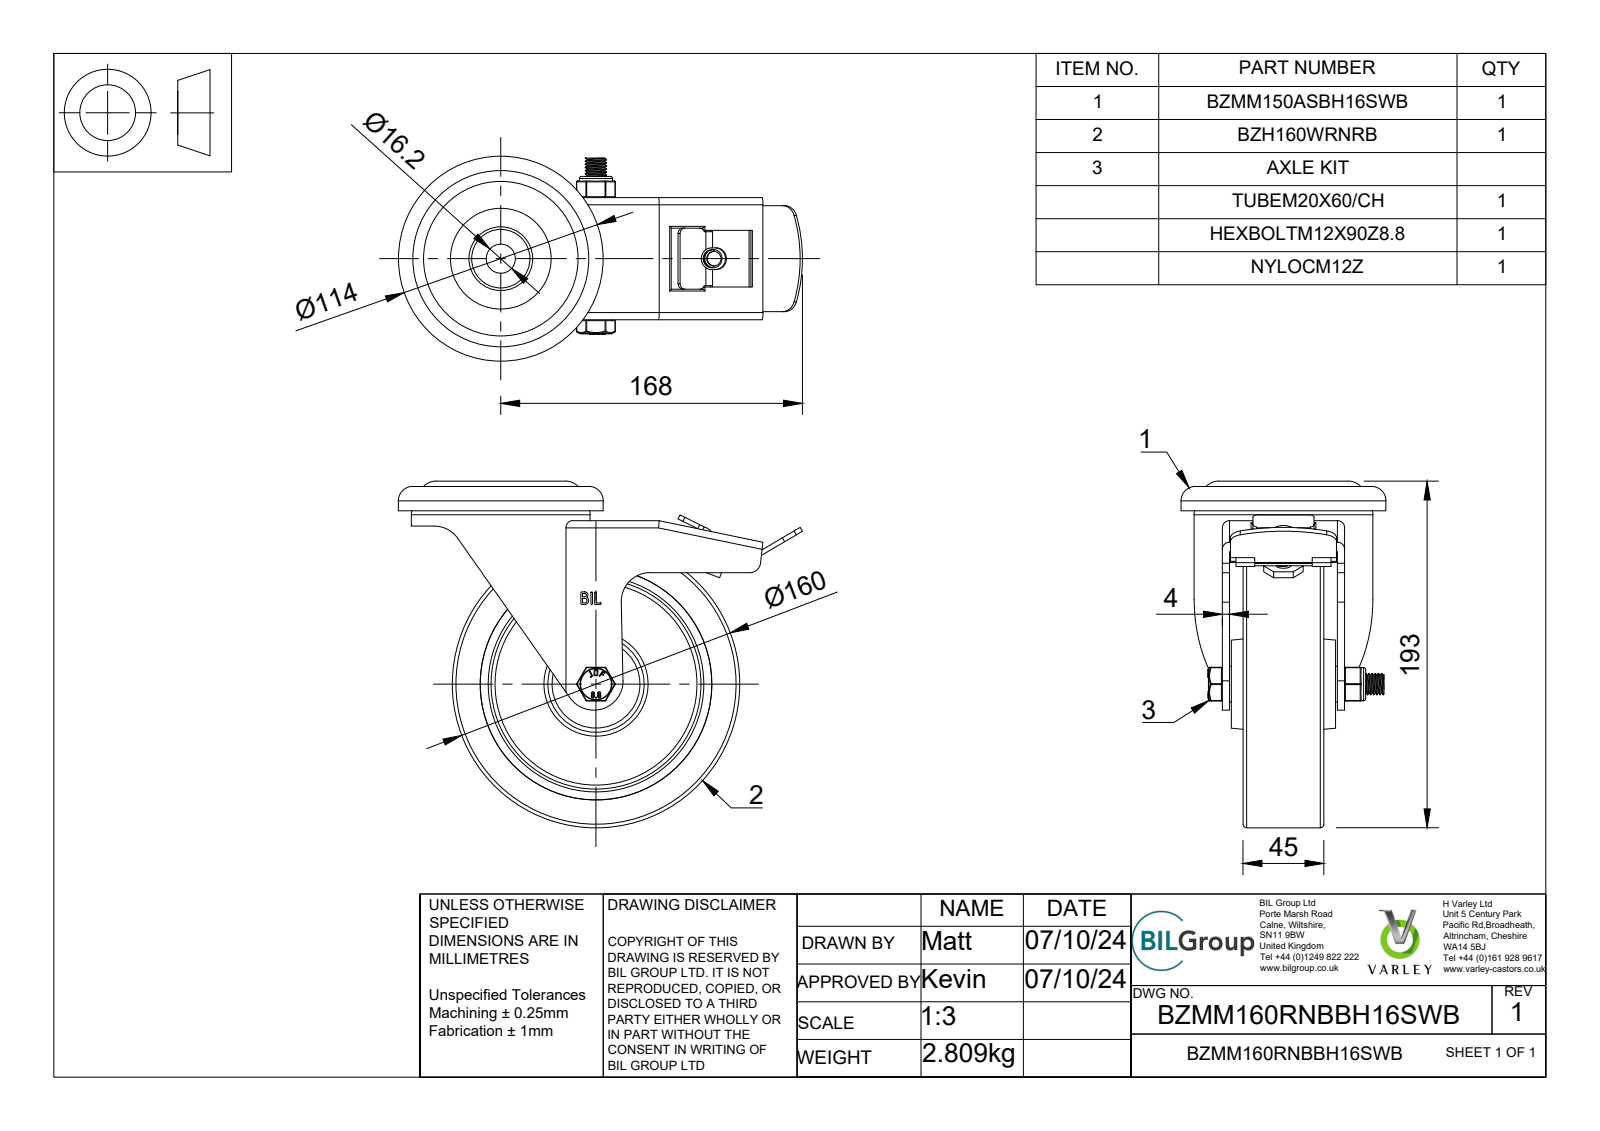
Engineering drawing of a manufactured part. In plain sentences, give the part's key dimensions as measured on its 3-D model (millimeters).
The part is named "BZMM160RNBBH16SWB v3; BZH160WRNRB v1; 75 SHORE A ELASTIC RUBBER TYRE; NYLON RIM (+7 more)". Its 3-D file was written by "Autodesk Translation Framework v13.20.0.188 (AUTOMOTIVE_DESIGN)". It is 24 solids with 653 faces: 352 planar, 205 cylindrical and 96 other. Overall it measures 225 by 193 by 114 millimeters. Its volume is 838 592 cubic millimeters and its surface area 280 180 square millimeters. Round holes: 1 of diameter 10, 1 of diameter 10.27, 1 of diameter 12, 1 of diameter 12.2, 1 of diameter 12.5, 1 of diameter 14, 1 of diameter 16.2, 1 of diameter 20, 1 of diameter 21, 1 of diameter 22, 1 of diameter 30, 1 of diameter 36.5. Round bosses or shafts: 10 of diameter 5, 1 of diameter 160, 1 of diameter 114, 1 of diameter 99.5, 1 of diameter 74, 1 of diameter 47, 1 of diameter 32.5, 1 of diameter 29.5. Partial cylindrical surfaces (rounded edges, fillets, slot ends): 24 of radius 0.5, 8 of radius 2, 6 of radius 1, 4 of radius 0.47, 4 of radius 0.9, 4 of radius 3, 4 of radius 4, 3 of radius 6. The main face-to-face distances are 26.5, 18.5, 4, 8, 26, 1, 7.5, 52.5, 34, 45.
